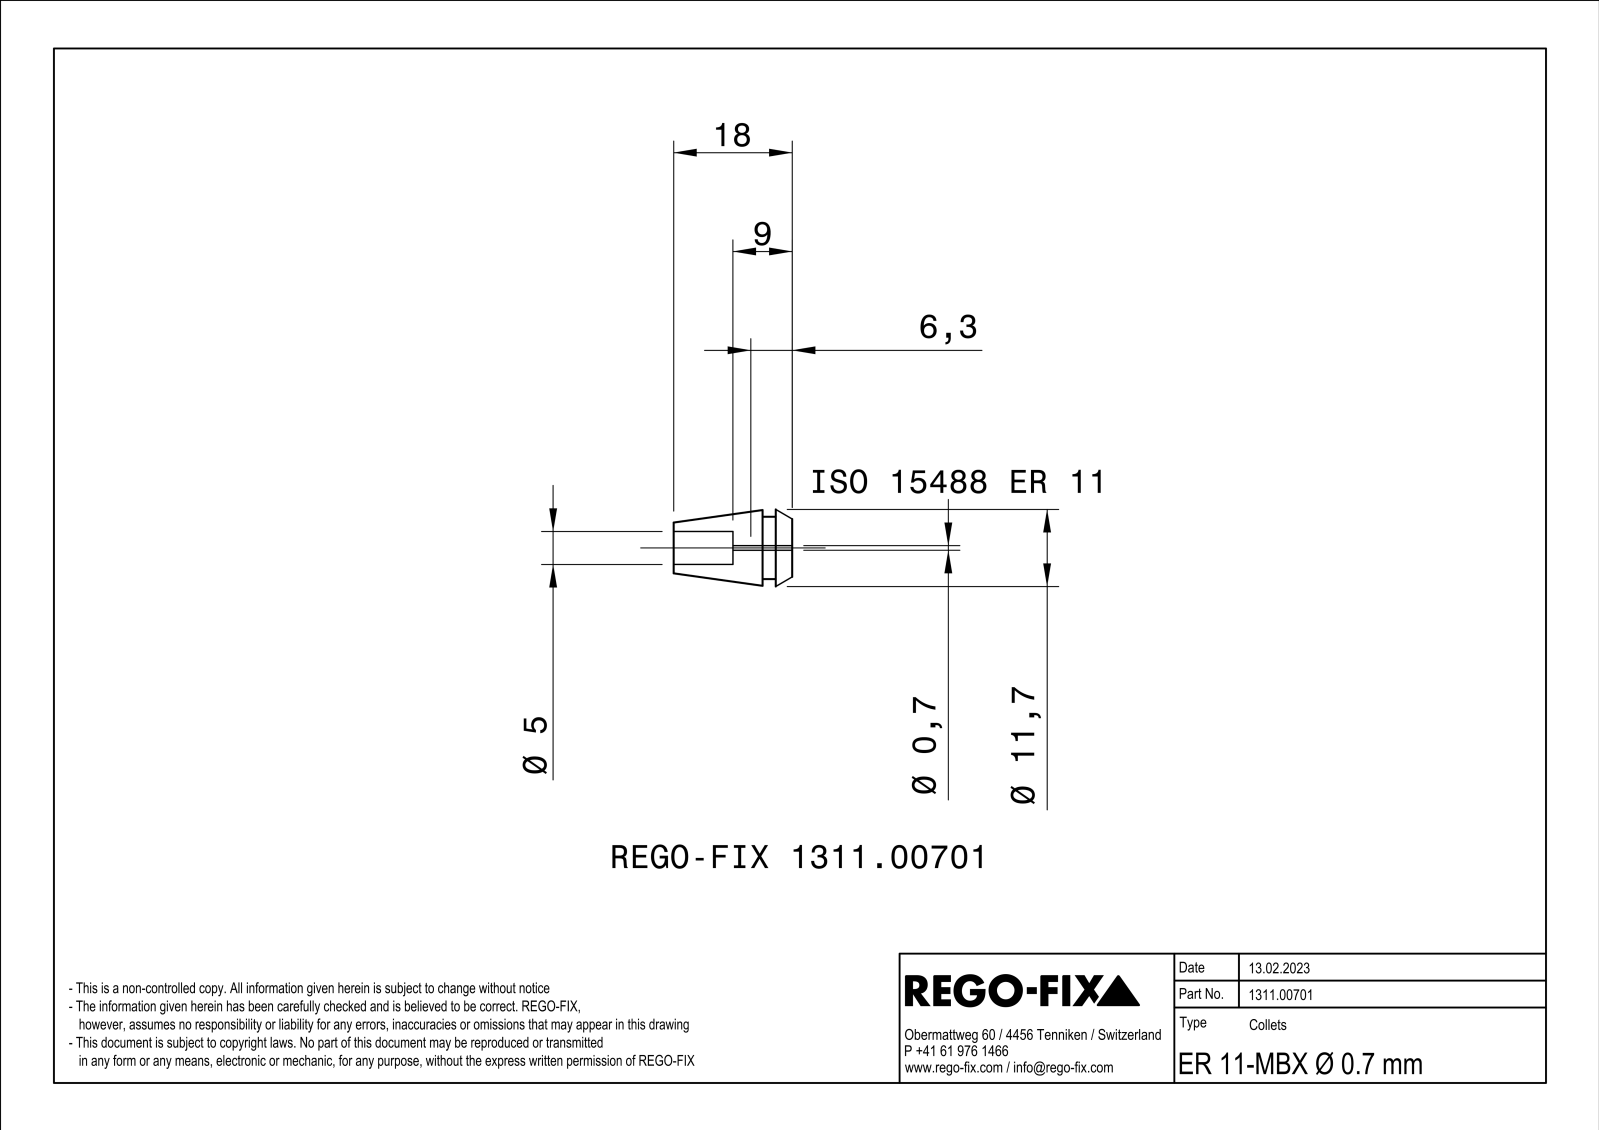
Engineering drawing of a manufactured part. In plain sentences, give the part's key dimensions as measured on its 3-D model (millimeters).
The part is named "NOCUT". Its 3-D file was written by "SIEMENS PLM Software Solid Edge ST10 (AUTOMOTIVE_DESIGN)". It is 1 solid with 91 faces: 26 planar, 19 cylindrical and 46 other. Overall it measures 18 by 11.41 by 11.39 millimeters. Its volume is 991 cubic millimeters and its surface area 1 256 square millimeters. Round holes: 3 of diameter 1.5, 1 of diameter 5. Round bosses or shafts: 1 of diameter 9.5. Partial cylindrical surfaces (rounded edges, fillets, slot ends): 3 of radius 25, 1 of radius 0.35. The main face-to-face distances are 0.8, 4.5, 0.51, 9, 18, 13.5, 2.5, 2, 15.5, 6.5. The hole center spacings are 1.7, 2.94.
